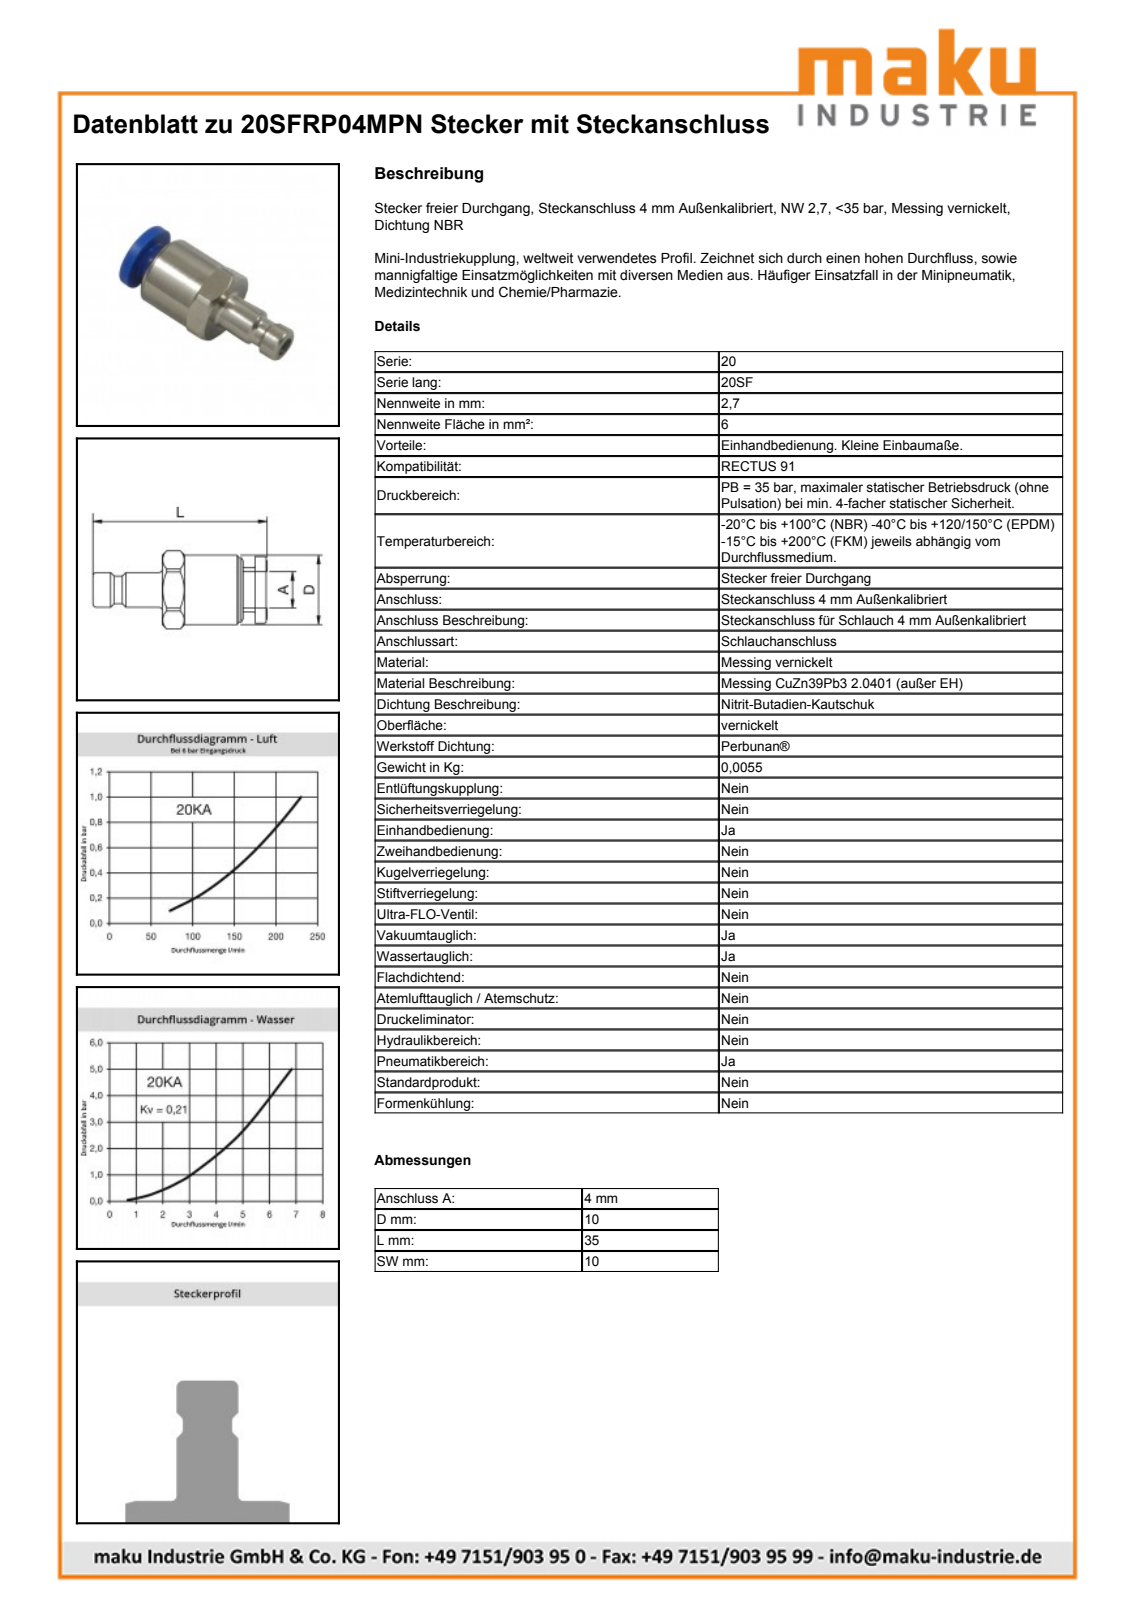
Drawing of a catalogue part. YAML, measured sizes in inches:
part_name: "D111967"
step_written_by: "Autodesk Inventor 2013 (AUTOMOTIVE_DESIGN)"
units: inches
bodies: {solids: 1, faces: 46, planar: 11, cylindrical: 13, other: 22}
overall_size: [1.004, 0.443, 0.394]
volume: 0.08
surface_area: 1.32
round_bosses_or_shafts:
  - {diameter: 0.394, count: 1}
  - {diameter: 0.378, count: 1}
  - {diameter: 0.364, count: 1}
  - {diameter: 0.252, count: 1}
  - {diameter: 0.197, count: 1}
  - {diameter: 0.156, count: 1}
partial_cylinders:
  - {radius: 0.221, count: 1}
face_to_face_distances: [0.394, 0.61, 0.059, 0.551, 0.138, 0.079, 0.472, 1.004, 0.945, 0.866]
